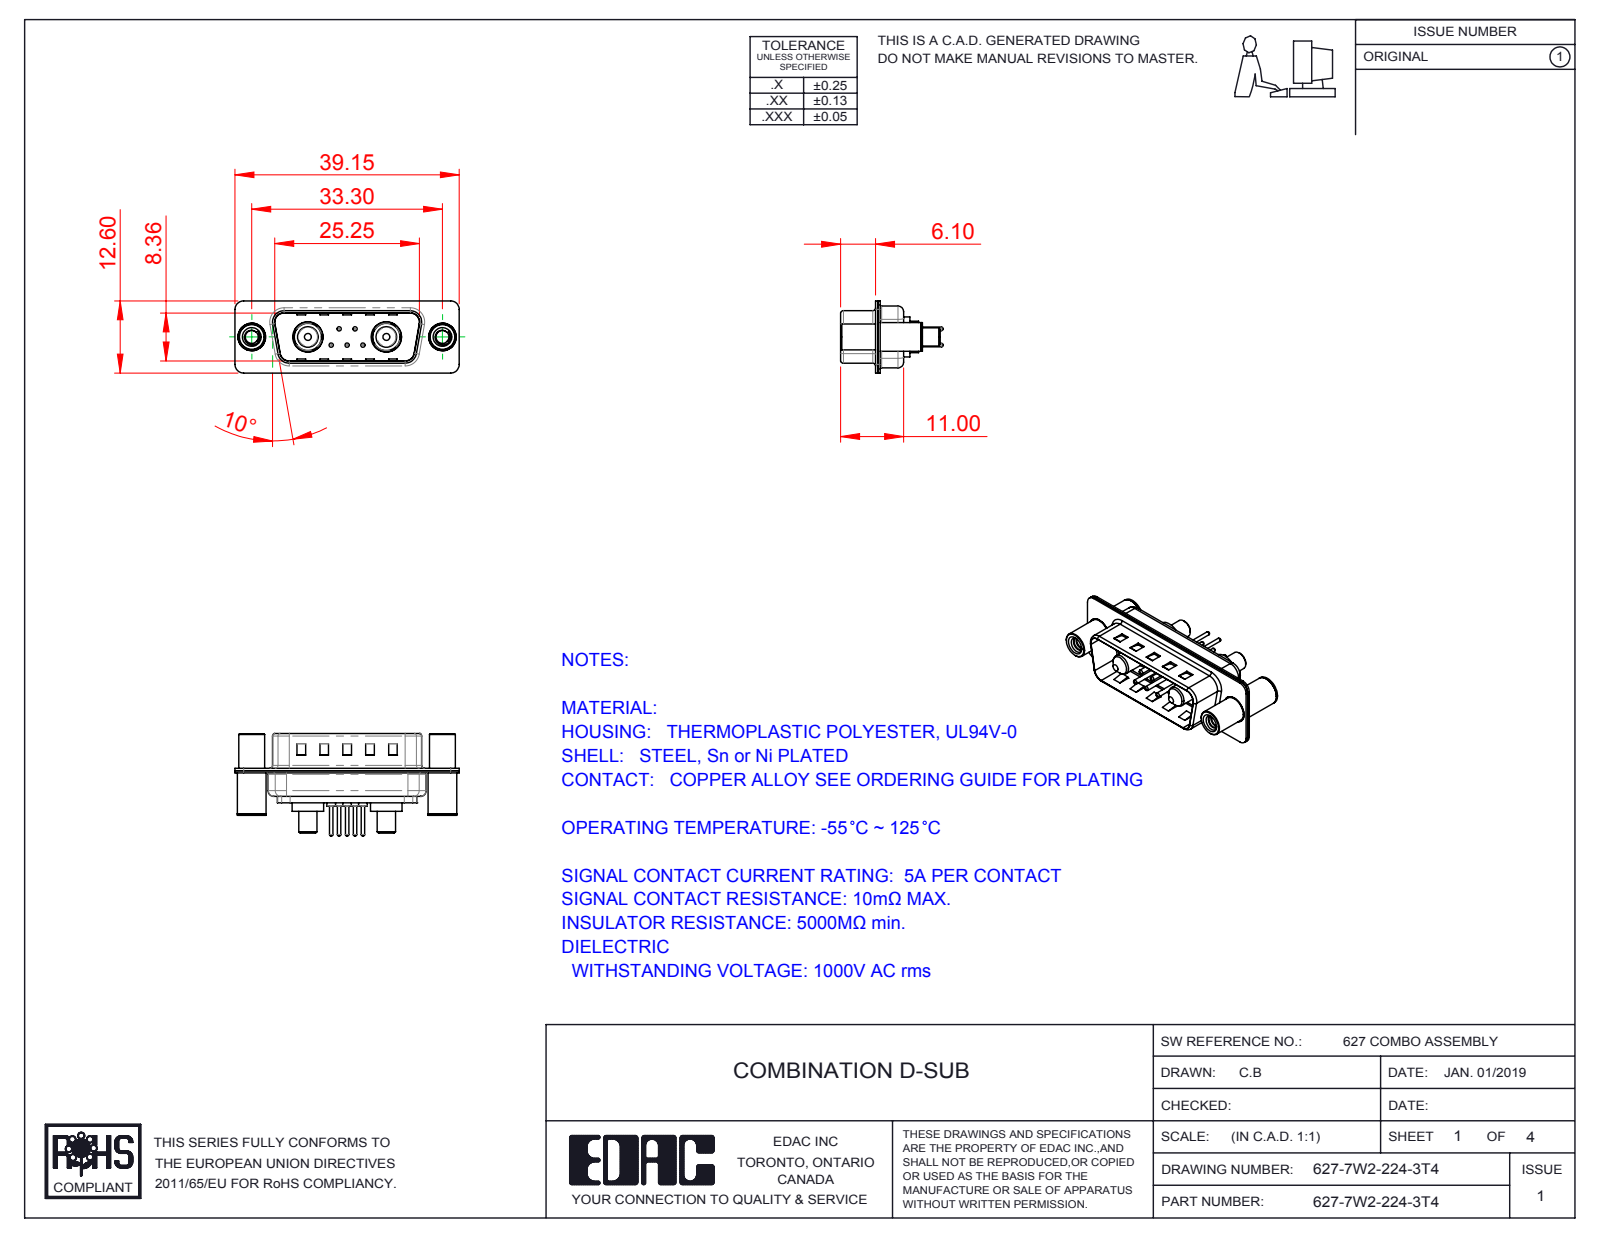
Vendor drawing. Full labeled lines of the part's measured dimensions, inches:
Part name (STEP PRODUCT): 627Combo Housing_7W2; 627Combo Contact Row 2_24; 627Combo Threaded Standoff and Board Spacer_4; 627-7W2-224-3T4 (+4 more)
STEP written by: SolidWorks 2016 (CONFIG_CONTROL_DESIGN)
Units: inches
Bodies: 14 solids, 691 faces (200 planar, 293 cylindrical, 198 other)
Overall size (bounding box): 1.541 × 0.705 × 0.496
Volume: 0.139 in³ · Surface area: 8.19 in²
Round holes (diameter × count): ⌀0.03 ×5, ⌀0.063 ×5, ⌀0.079 ×5, ⌀0.089 ×2, ⌀0.128 ×2, ⌀0.157 ×2, ⌀0.189 ×2, ⌀0.191 ×2, ⌀0.209 ×2
Round bosses / shafts (diameter × count): ⌀0.059 ×5, ⌀0.024 ×5, ⌀0.217 ×2, ⌀0.205 ×2, ⌀0.197 ×2, ⌀0.193 ×2, ⌀0.187 ×2, ⌀0.177 ×2
Partial cylindrical surfaces — rounded edges, fillets, slot ends (radius × count): R0.059 ×20, R0.079 ×12, R0.02 ×8, R0.063 ×8, R0.01 ×4, R0.024 ×4, R0.026 ×4, R0.035 ×4
Main face-to-face distances: 0.016, 0.032, 0.377, 0.031, 0.345, 0.059, 0.22, 0.236, 0.205, 0.386
Hole centre spacings: 0.124, 0.109, 0.386, 0.925, 0.17, 0.17, 0.198, 0.198
